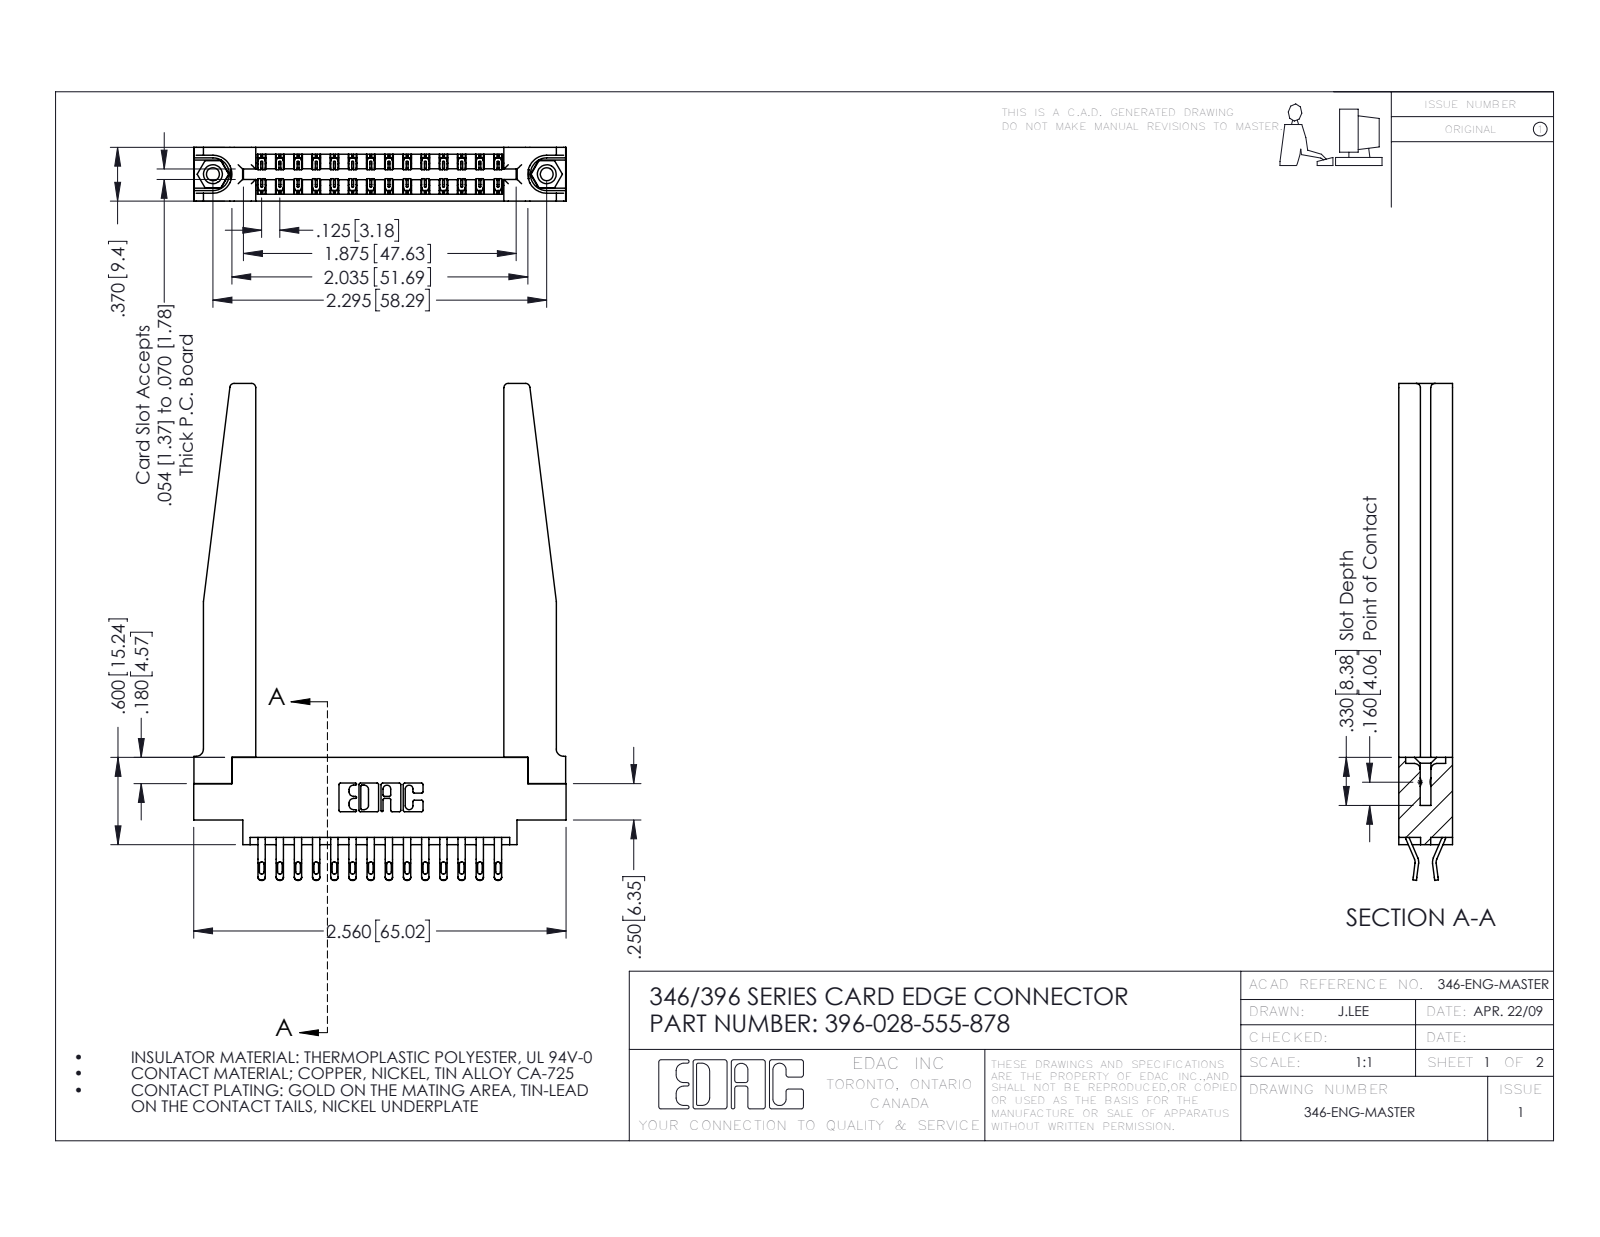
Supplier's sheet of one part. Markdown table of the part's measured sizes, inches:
| quantity | value |
| --- | --- |
| part name | 346-220-078_345-220-078; 345-250-001_345-250-001-102; 345-292-001_555 Tail; 346 Part_0.170 Offset - 0.156 Dia-TH (+1 more) |
| STEP written by | SolidWorks 2016 (CONFIG_CONTROL_DESIGN) |
| units | inches |
| bodies | 33 solids, 1984 faces (1146 planar, 786 cylindrical, 52 other) |
| overall size | 3.415 × 2.56 × 0.37 |
| volume | 0.791 in³ |
| surface area | 23.07 in² |
| round holes (diameter × count) | 0.089 × 2, 0.125 × 2, 0.156 × 2, 0.064 × 1 |
| round bosses / shafts (diameter × count) | 0.155 × 2 |
| partial cylindrical surfaces (radius × count) | 0.016 × 56, 0.02 × 56, 0.006 × 42, 0.01 × 22, 0.03 × 8, 0.007 × 6, 0.031 × 6, 0.05 × 4 |
| main face-to-face distances | 0.37, 0.15, 0.072, 0.148, 0.048, 0.322, 0.25, 0.102, 0.22, 0.173 |
| hole center spacings | 0.246, 2.089, 2.295 |
